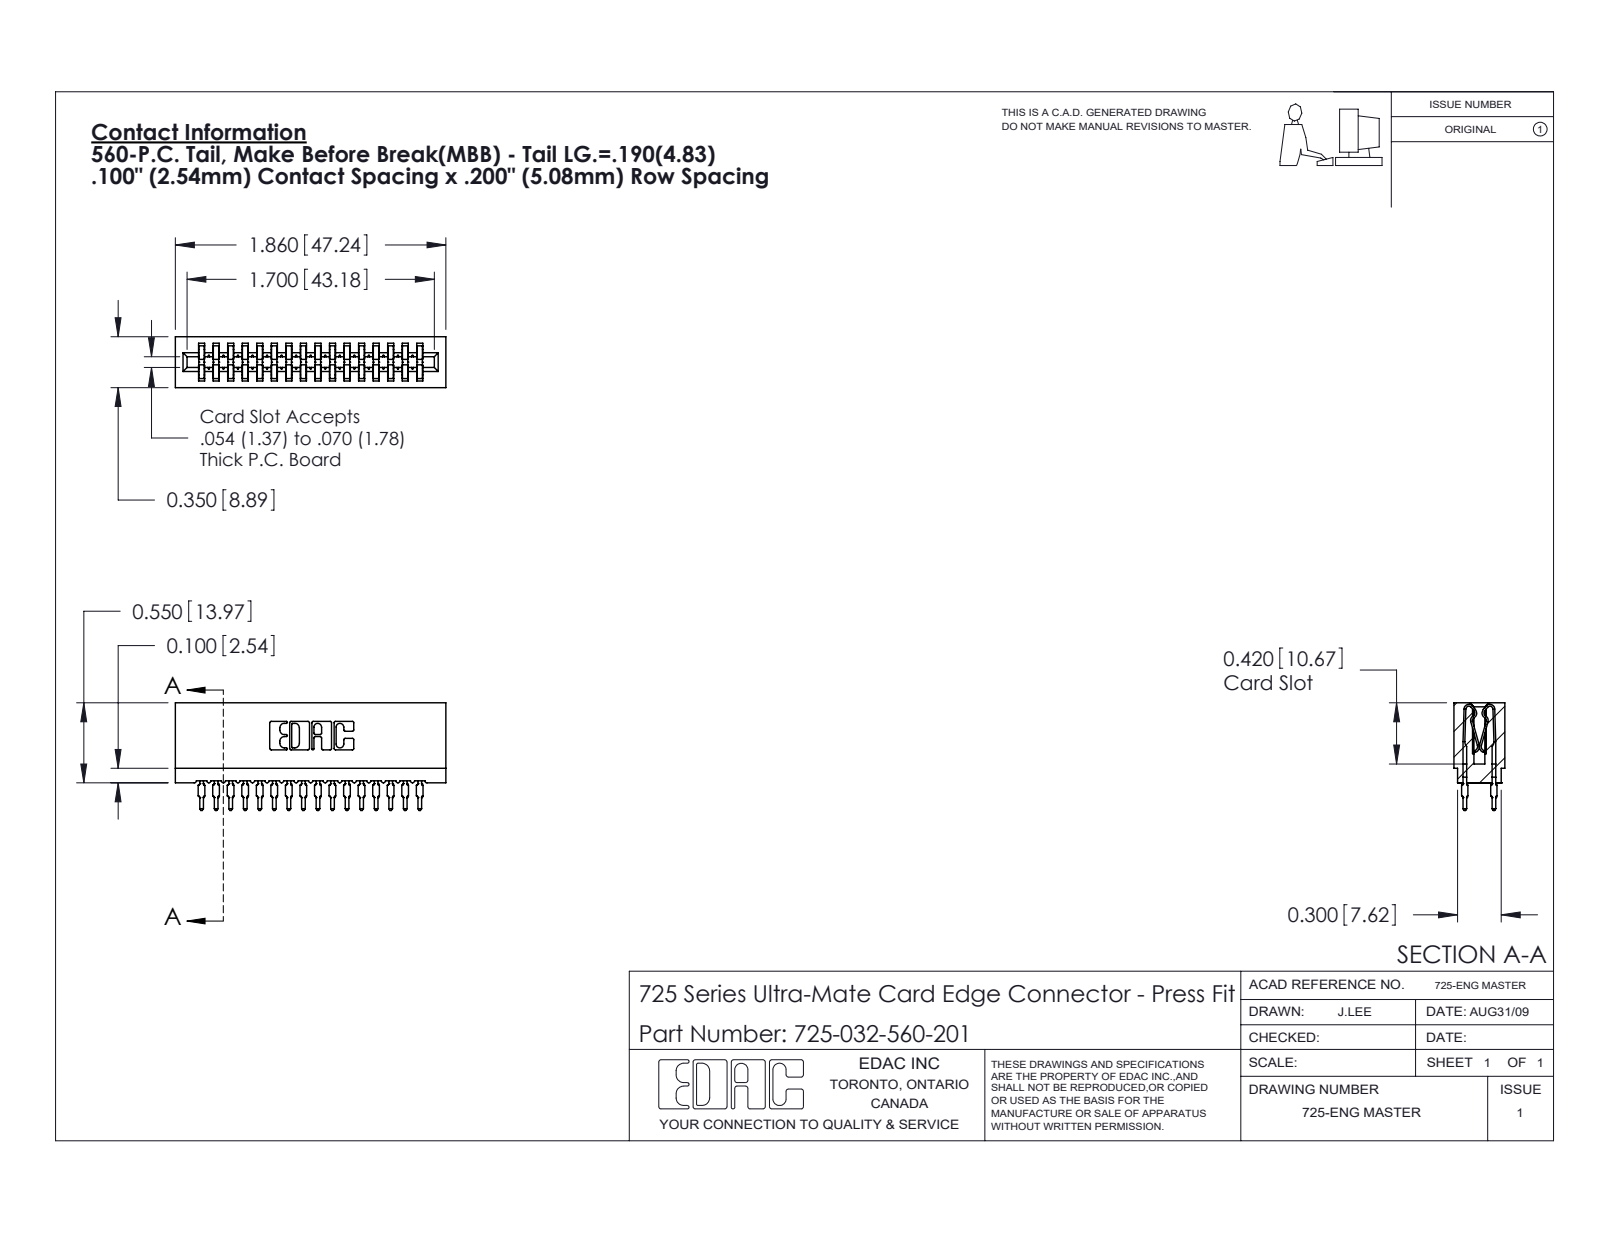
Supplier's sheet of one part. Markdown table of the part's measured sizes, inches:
| quantity | value |
| --- | --- |
| part name | 745-292-001_560; 725-032-560-201; 725 Part_Insulator Option - 01 |
| STEP written by | SolidWorks 2020 (CONFIG_CONTROL_DESIGN) |
| units | inches |
| bodies | 33 solids, 3247 faces (1687 planar, 728 cylindrical, 832 other) |
| overall size | 1.86 × 0.741 × 0.35 |
| volume | 0.244 in³ |
| surface area | 13 in² |
| partial cylindrical surfaces (radius × count) | 0.021 × 64, 0.015 × 32, 0.01 × 22, 0.005 × 8, 0.011 × 8, 0.007 × 6, 0.031 × 6, 0.026 × 3 |
| main face-to-face distances | 0.2, 0.1, 0.3, 0.4, 0.5, 0.6, 0.35, 0.063, 0.287, 0.7 |
